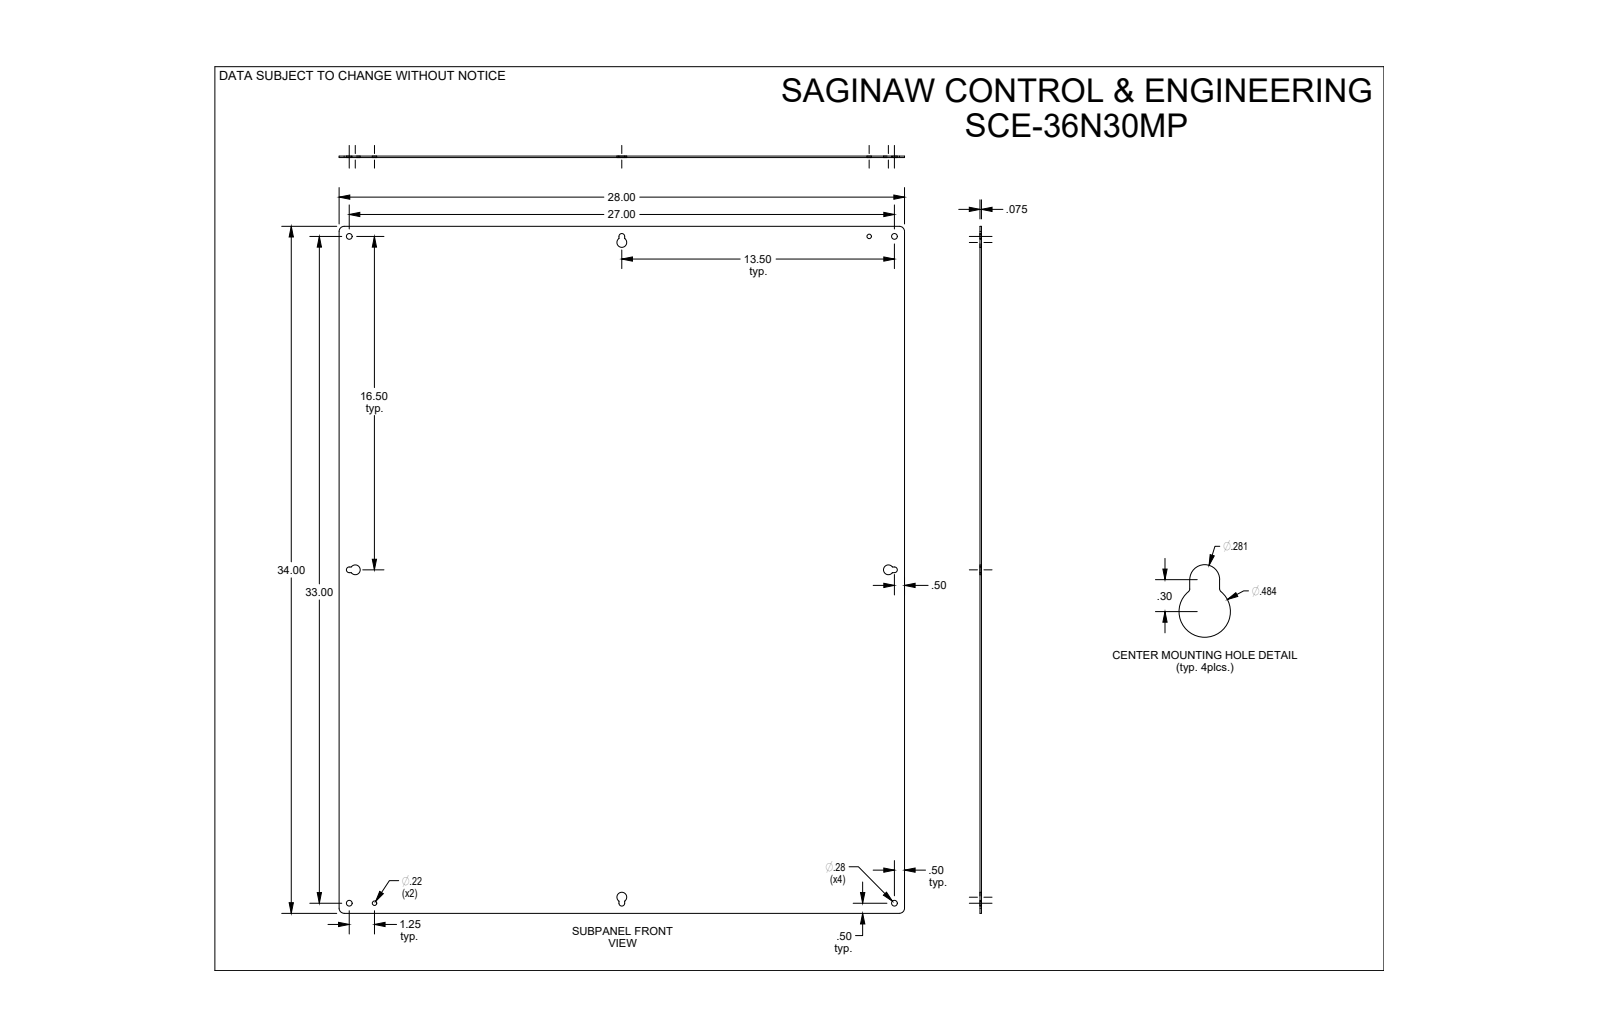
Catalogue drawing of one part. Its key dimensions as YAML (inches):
part_name: "SCE-36N30MP"
step_written_by: "SolidWorks 2019 (CONFIG_CONTROL_DESIGN)"
units: inches
bodies: {solids: 1, faces: 40, planar: 14, cylindrical: 26, other: 0}
overall_size: [34, 28, 0.075]
volume: 71.3
surface_area: 1912
round_holes:
  - {diameter: 0.281, count: 4}
  - {diameter: 0.218, count: 2}
partial_cylinders:
  - {radius: 0.03, count: 8}
  - {radius: 0.141, count: 4}
  - {radius: 0.242, count: 4}
  - {radius: 0.25, count: 4}
face_to_face_distances: [0.075, 28, 34, 16.859, 17.141, 0.281, 13.859, 14.141]
hole_center_spacings: [1.25, 25.75, 27, 33, 33.024, 41.857, 42.638, 41.1]
